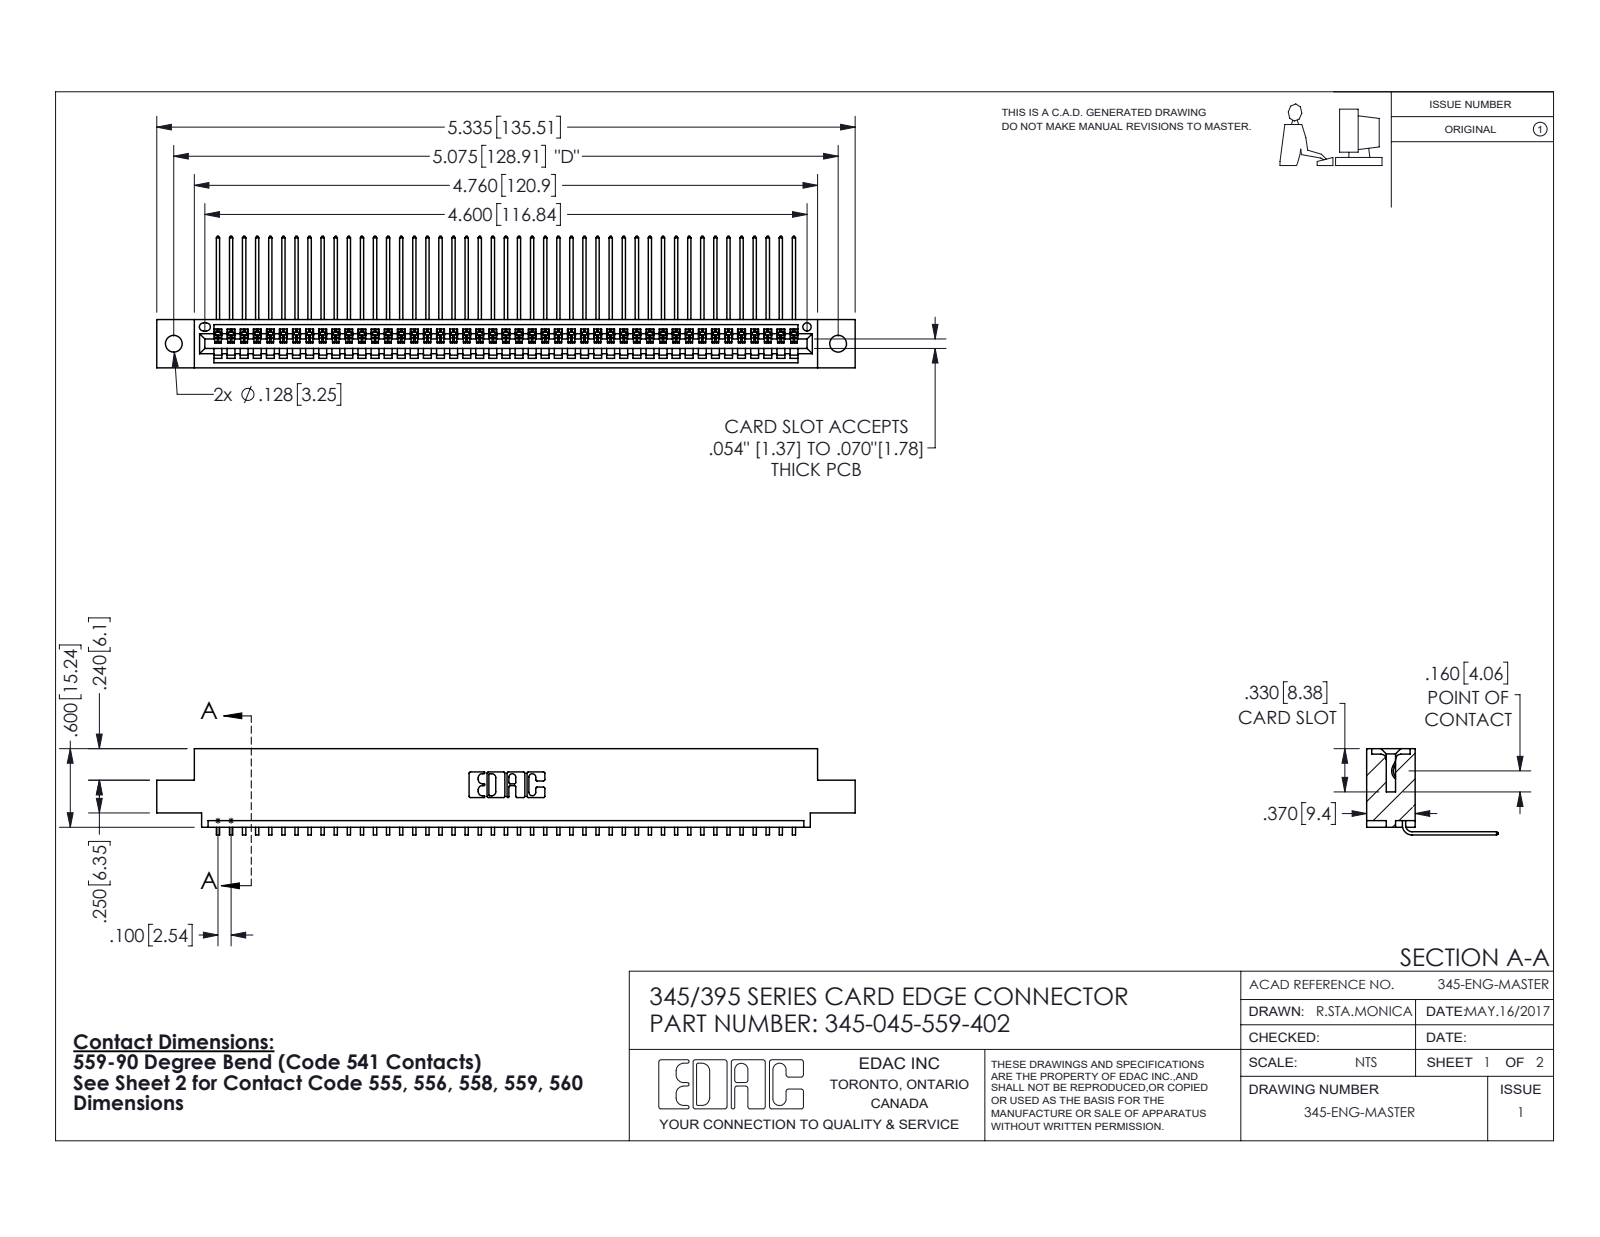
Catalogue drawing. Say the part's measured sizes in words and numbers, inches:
The part is named "345-292-001_558 559 Tail - 1; 345-045-559-402; 345 Part_0.110 Offset - 0.128 Dia". Its 3-D file was written by "SolidWorks 2016 (CONFIG_CONTROL_DESIGN)". It is 46 solids with 2830 faces: 1974 planar, 856 cylindrical and 0 other. Overall it measures 5.335 by 1.005 by 0.659 inches. Its volume is 0.789 cubic inches and its surface area 27.78 square inches. Round holes: 2 of diameter 0.128, 1 of diameter 0.064. Partial cylindrical surfaces (rounded edges, fillets, slot ends): 90 of radius 0.006, 22 of radius 0.01, 6 of radius 0.007, 6 of radius 0.031, 3 of radius 0.026, 2 of radius 0.031, 2 of radius 0.04, 1 of radius 0.014. The main face-to-face distances are 0.072, 0.298, 0.37, 0.2, 0.098, 0.272, 0.025, 0.225, 0.149, 0.072. The hole center spacings are 0.27, 4.839, 5.075.
